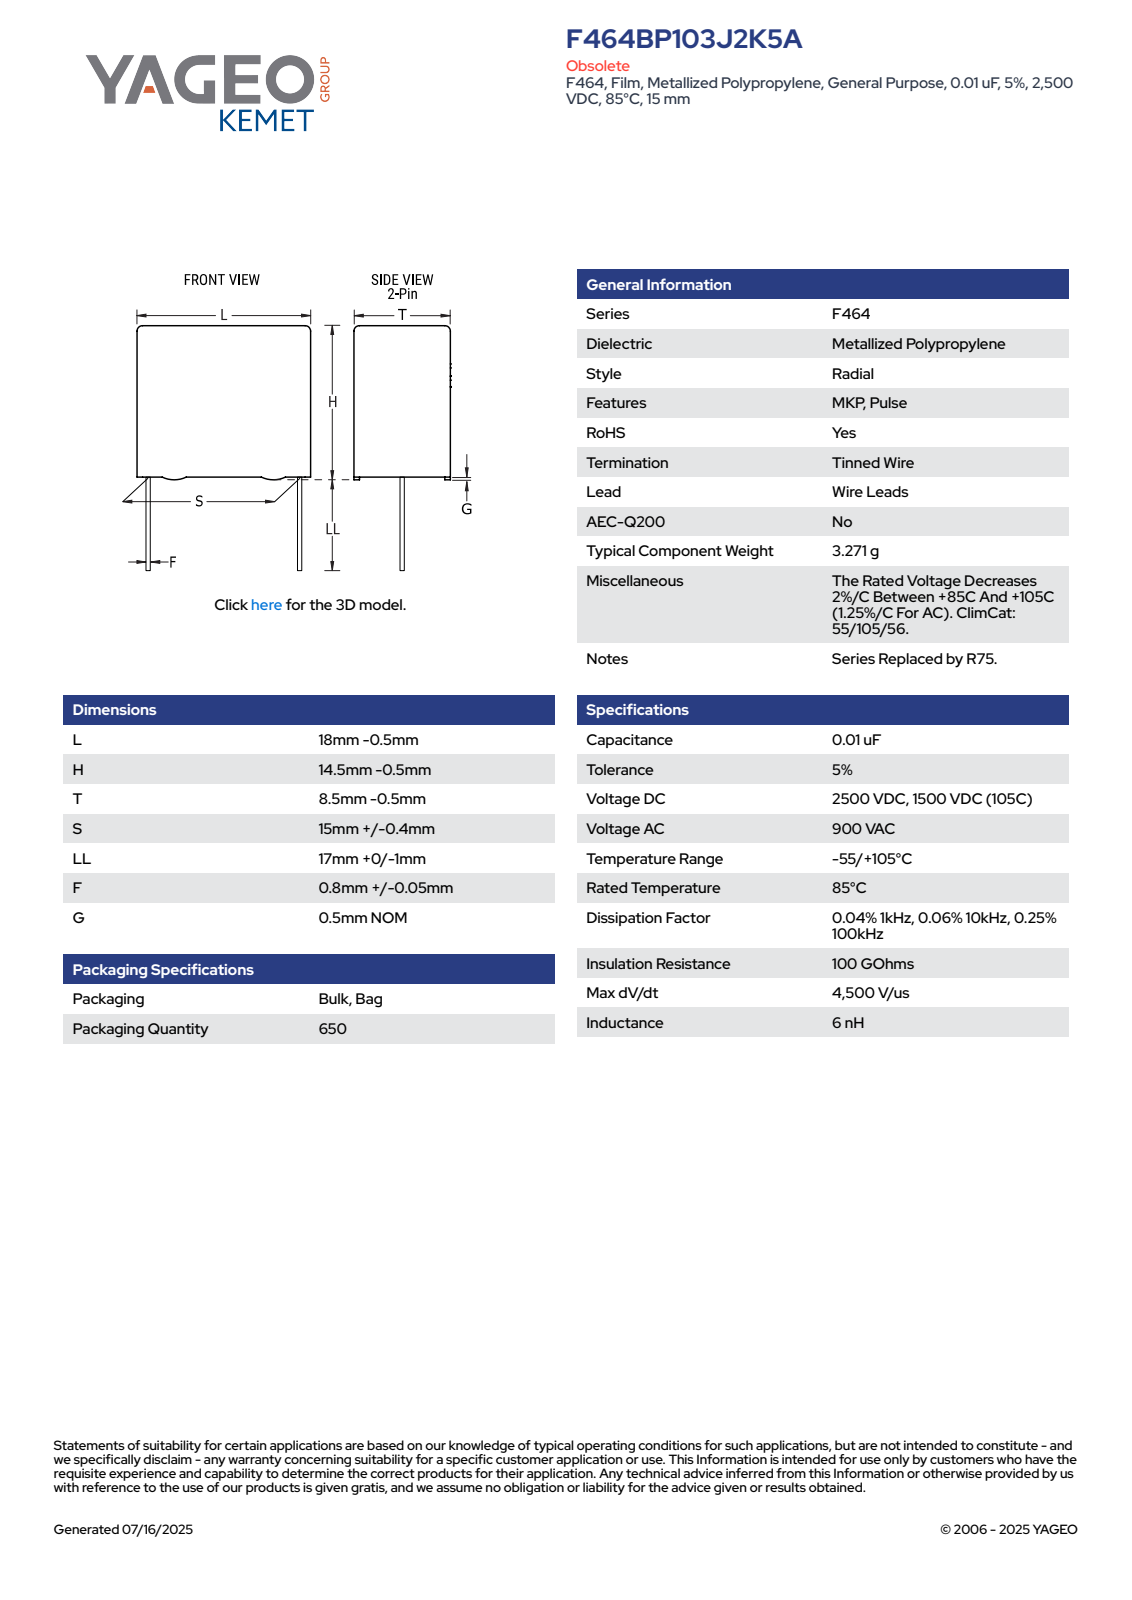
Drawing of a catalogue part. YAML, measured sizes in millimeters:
part_name: "CFR_RBG_18X14.5X8.5_L17.5H14T8S15LL17F0.85G0.5"
step_written_by: "SolidWorks 2014 (AUTOMOTIVE_DESIGN)"
units: millimeters
bodies: {solids: 4, faces: 89, planar: 81, cylindrical: 8, other: 0}
overall_size: [31, 17.5, 8.01]
volume: 1910
surface_area: 1097
round_bosses_or_shafts:
  - {diameter: 0.85, count: 2}
partial_cylinders:
  - {radius: 0.5, count: 4}
face_to_face_distances: [8, 13.5, 17.5, 8.01, 0.46, 7.54, 0.5, 14, 0.47, 7.08]
